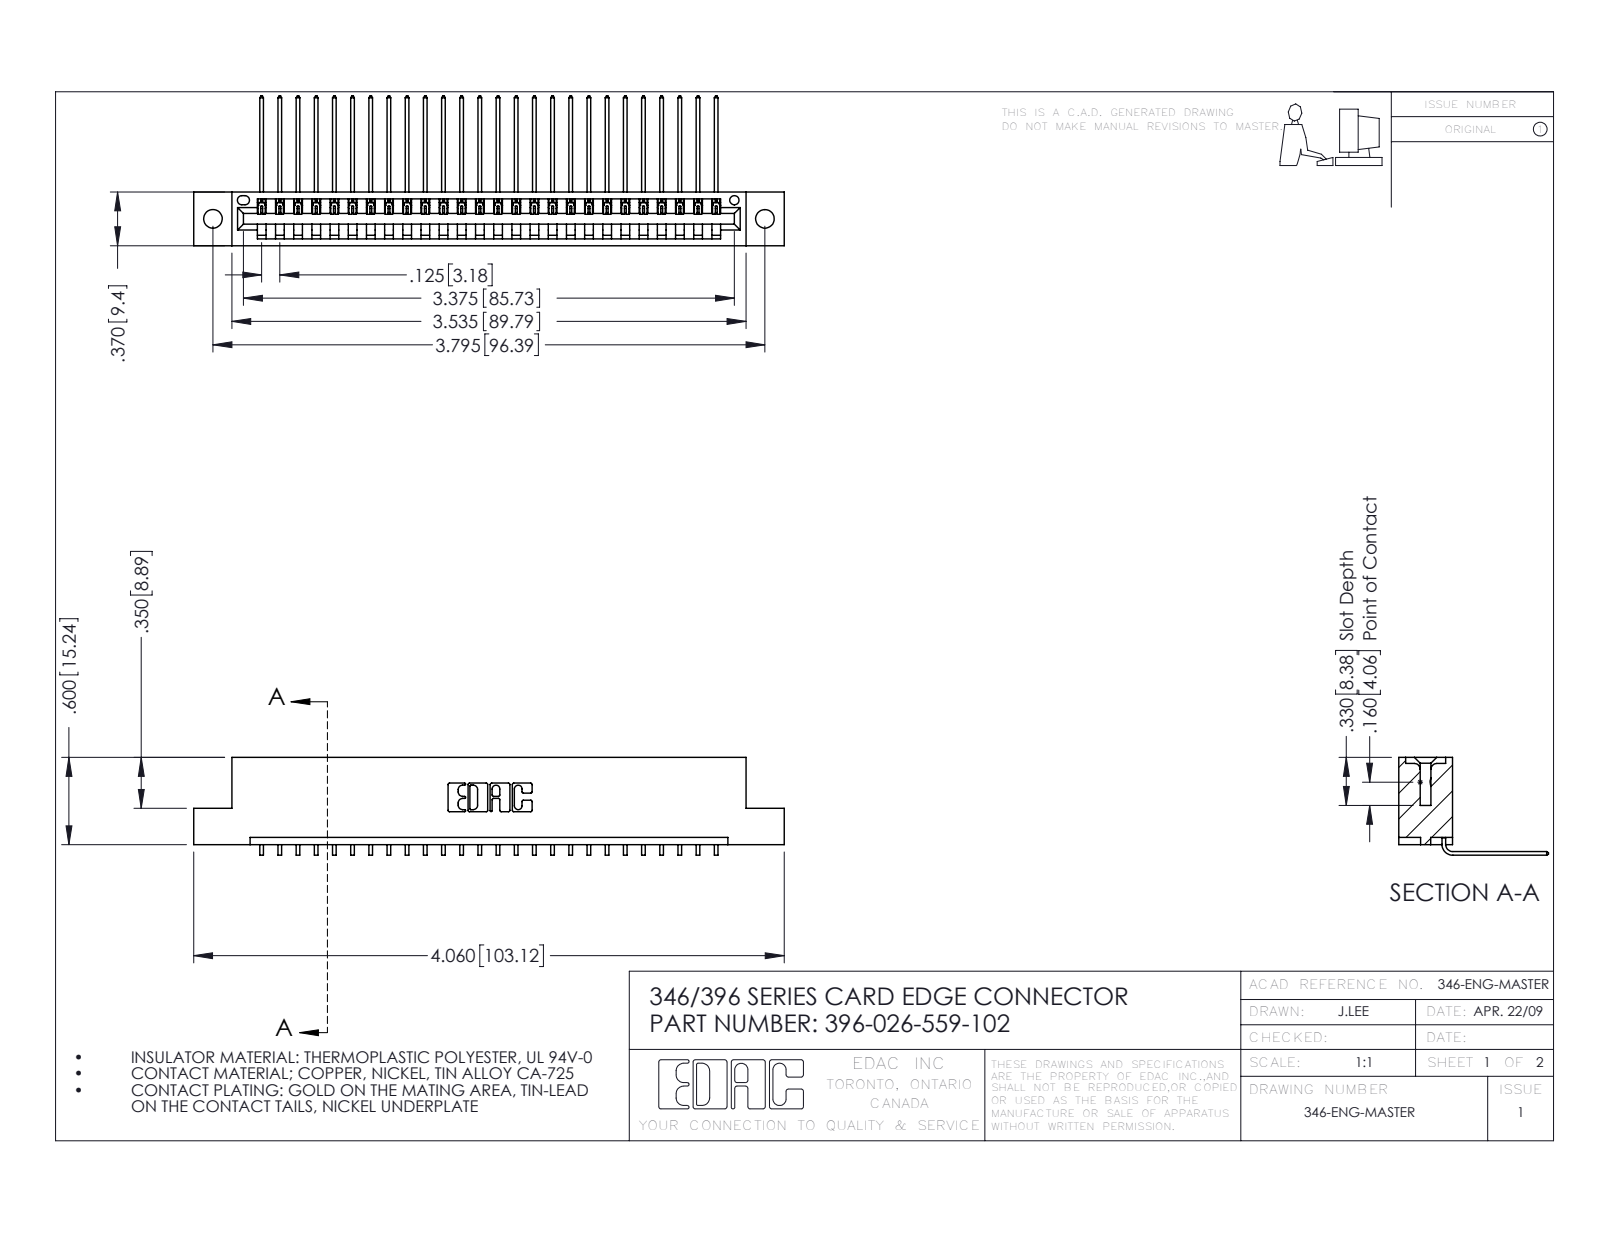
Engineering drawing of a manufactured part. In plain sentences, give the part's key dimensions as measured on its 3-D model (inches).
The part is named "346 Part_Flush Mounting Lugs - 0.128 Dia; 396-026-559-102; 345-292-001_558 559 Tail - 1". Its 3-D file was written by "SolidWorks 2016 (CONFIG_CONTROL_DESIGN)". It is 27 solids with 1682 faces: 1168 planar, 514 cylindrical and 0 other. Overall it measures 4.06 by 1.03 by 0.673 inches. Its volume is 0.599 cubic inches and its surface area 19.12 square inches. Round holes: 2 of diameter 0.128, 1 of diameter 0.064. Partial cylindrical surfaces (rounded edges, fillets, slot ends): 52 of radius 0.006, 22 of radius 0.01, 6 of radius 0.007, 6 of radius 0.031, 3 of radius 0.026, 2 of radius 0.031, 2 of radius 0.04, 1 of radius 0.014. The main face-to-face distances are 0.048, 0.322, 0.37, 0.25, 0.072, 0.025, 0.298, 0.148, 0.222, 0.1. The hole center spacings are 0.246, 3.587, 3.795.
